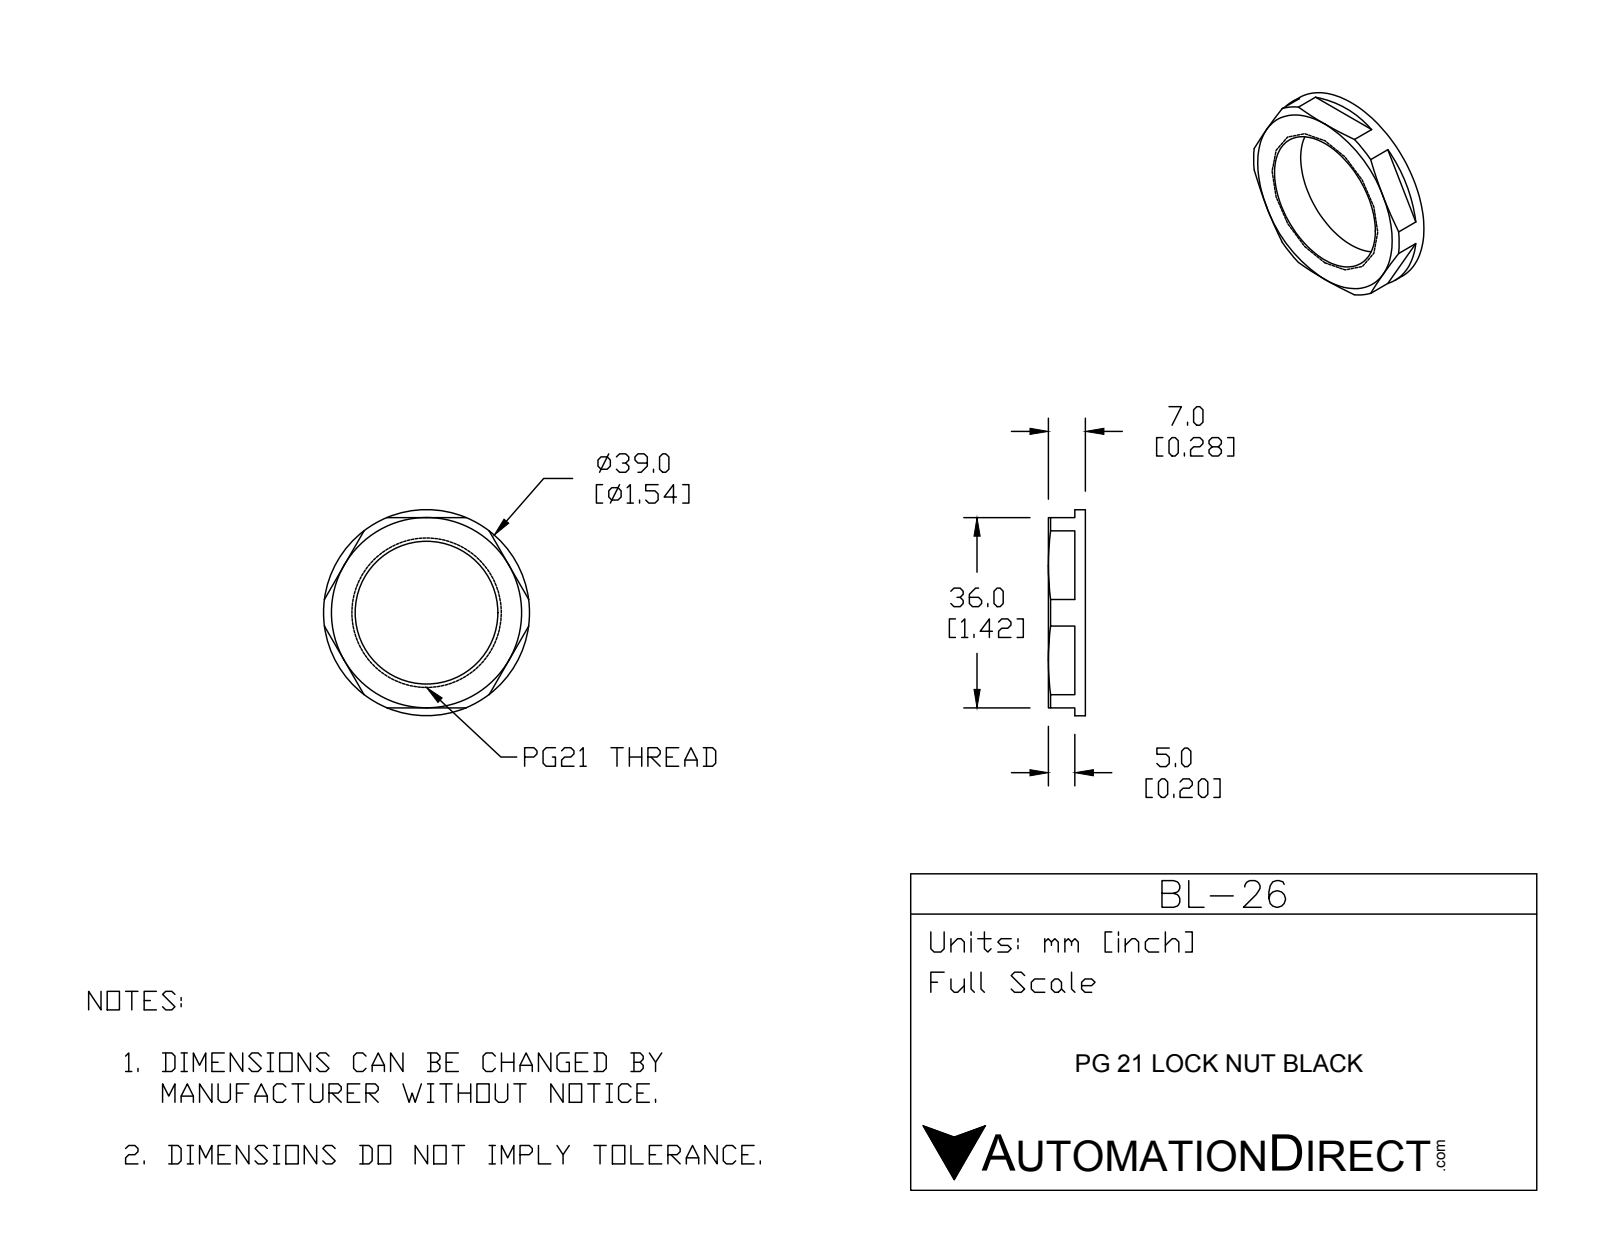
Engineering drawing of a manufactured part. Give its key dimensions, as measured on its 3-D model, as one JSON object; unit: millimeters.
{"part_name": "BL-26", "step_written_by": "SolidWorks 2015 (CONFIG_CONTROL_DESIGN)", "units": "millimeters", "bodies": {"solids": 1, "faces": 33, "planar": 17, "cylindrical": 10, "other": 6}, "overall_size": [39, 39, 7], "volume_mm3": 3885, "surface_area_mm2": 2666, "round_holes": [[1.5, 3], [27, 1]], "round_bosses_or_shafts": [[39, 1]], "face_to_face_distances": [7, 36, 2, 5, 1.7, 6.7], "hole_center_spacings": [18.05, 31.26, 31.27]}
